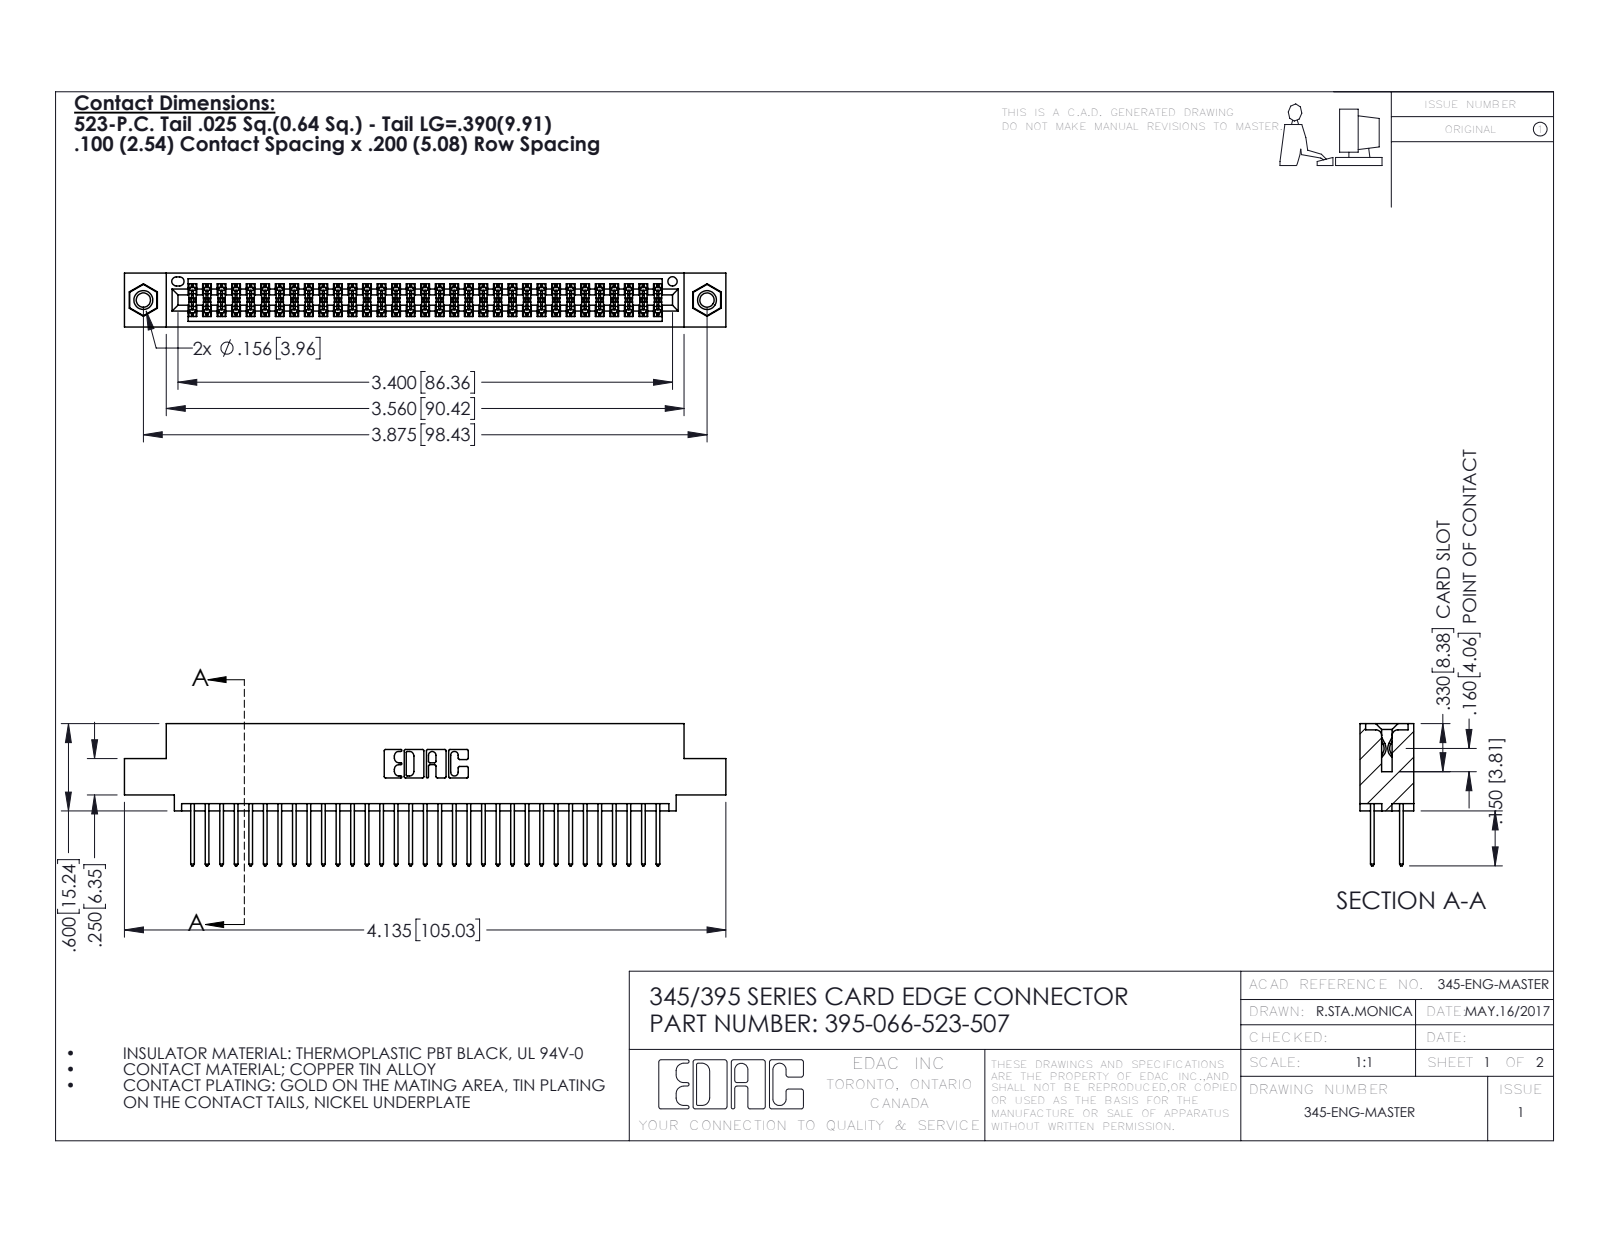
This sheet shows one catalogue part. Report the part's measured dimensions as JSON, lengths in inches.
{"part_name": "345 Part_0.110 Offset - 0.156 Dia-TI; 345-250-001_345-250-005-103; 395-066-523-507; 345-292-001_345-293-123", "step_written_by": "SolidWorks 2016 (CONFIG_CONTROL_DESIGN)", "units": "inches", "bodies": {"solids": 69, "faces": 3490, "planar": 2294, "cylindrical": 1180, "other": 16}, "overall_size": [4.135, 0.977, 0.37], "volume_in3": 0.62, "surface_area_in2": 24.15, "round_holes": [[0.098, 2], [0.125, 2], [0.156, 2], [0.064, 1]], "round_bosses_or_shafts": [[0.155, 2]], "partial_cylinders_radius": [[0.006, 99], [0.01, 66], [0.01, 22], [0.007, 6], [0.031, 6], [0.026, 3], [0.014, 2], [0.019, 2]], "face_to_face_distances": [0.072, 0.298, 0.2, 0.098, 0.272, 0.025, 0.37, 0.225, 0.175, 0.149], "hole_center_spacings": [0.27, 3.64, 3.875]}
